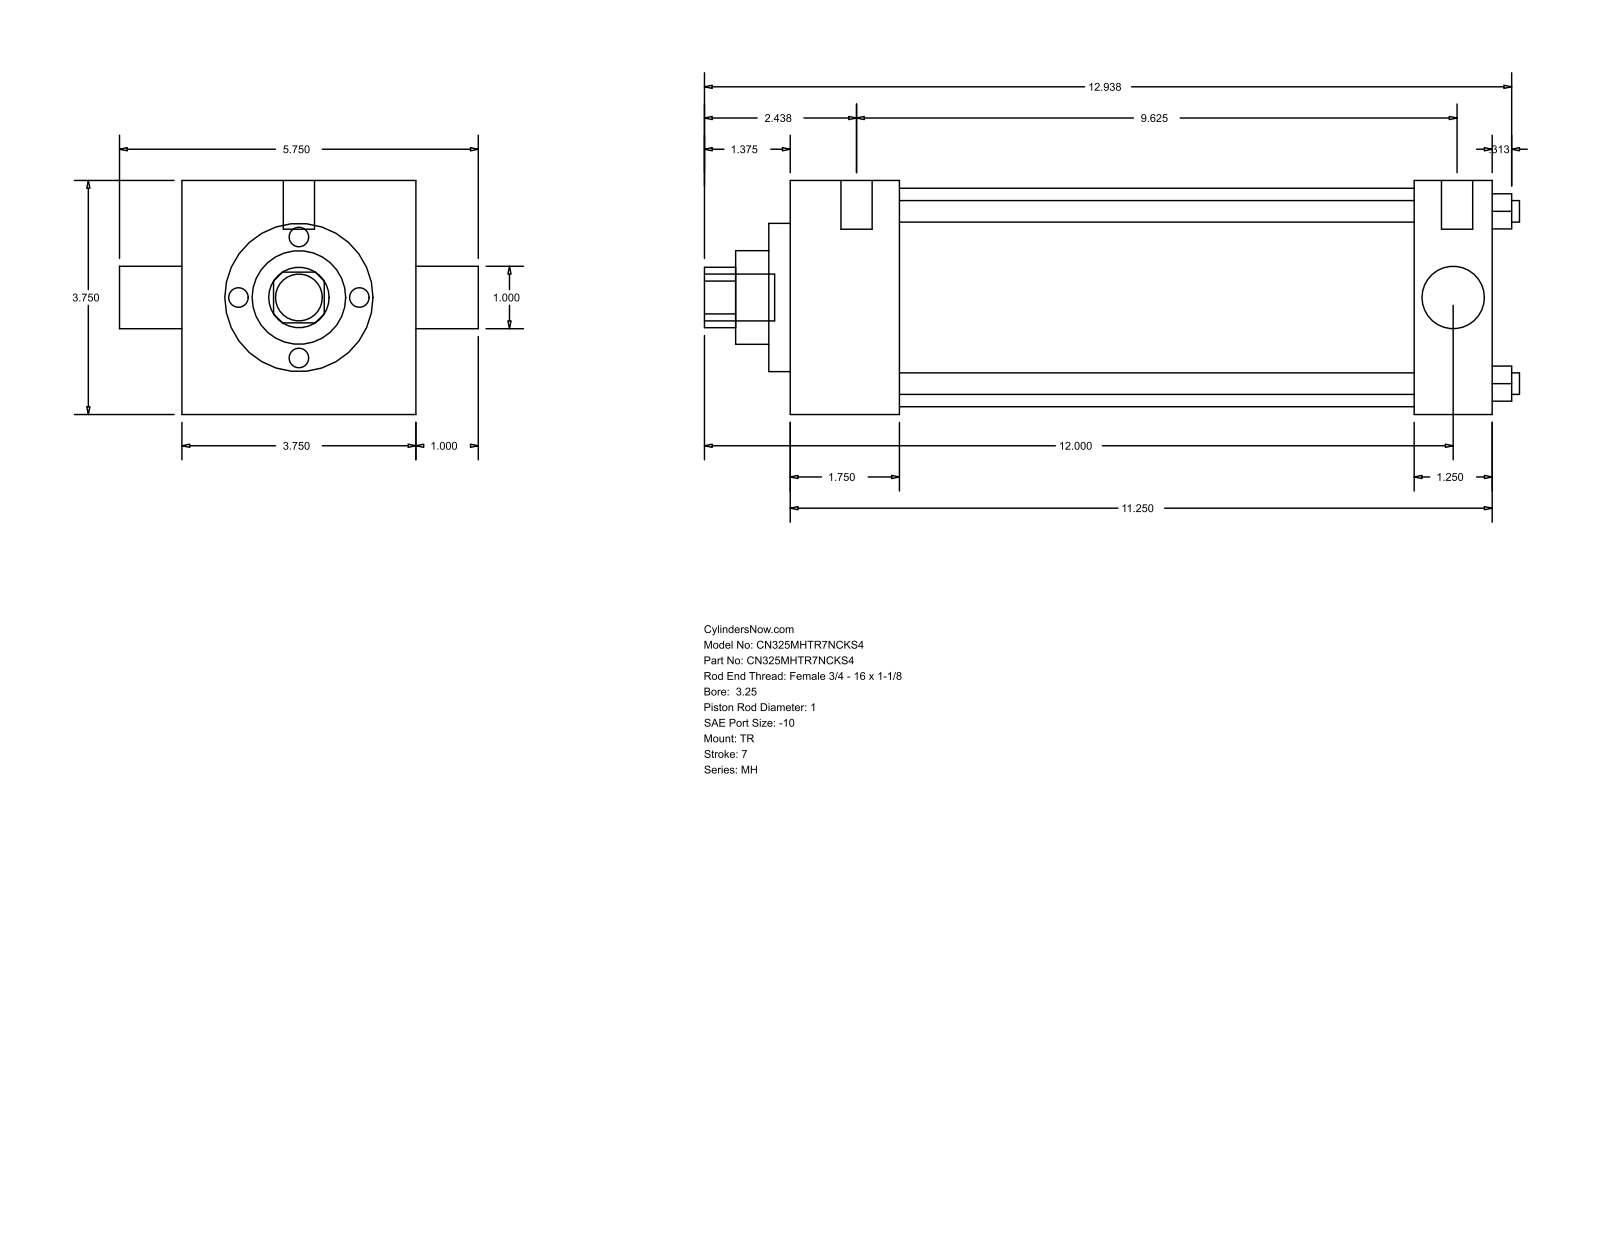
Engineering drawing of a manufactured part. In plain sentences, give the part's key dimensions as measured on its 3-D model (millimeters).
The part is named "MH_TR__0325_1". Its 3-D file was written by "GSSL Pune (CONFIG_CONTROL_DESIGN)". It is 0 solids with 86 faces: 61 planar, 25 cylindrical and 0 other. Overall it measures 331.79 by 146.05 by 95.25 millimeters. Round holes: 4 of diameter 8.76, 2 of diameter 25.4, 1 of diameter 38.1, 1 of diameter 60.33, 1 of diameter 88.9. Round bosses or shafts: 3 of diameter 5.56, 2 of diameter 12.7, 1 of diameter 19.05. Partial cylindrical surfaces (rounded edges, fillets, slot ends): 1 of radius 12.29. The main face-to-face distances are 95.24, 285.76, 44.46, 254.01, 209.55, 241.3, 31.75, 8.73, 53.19, 262.74. The hole center spacings are 49.57, 70.1, 99.14.
